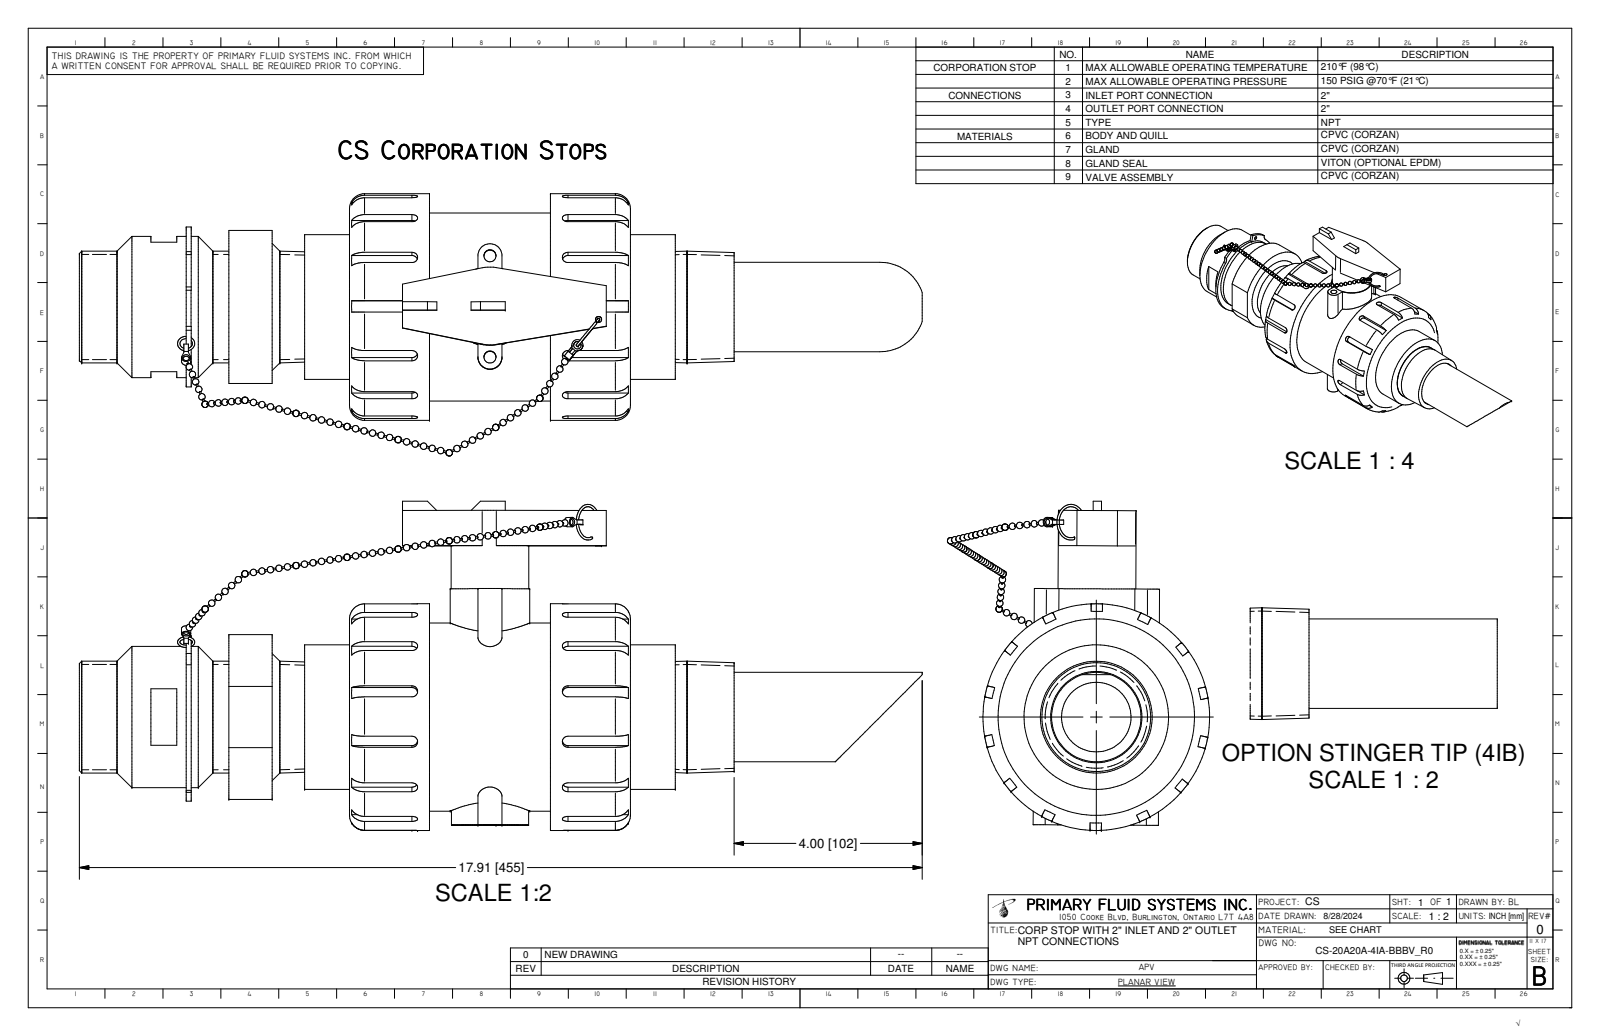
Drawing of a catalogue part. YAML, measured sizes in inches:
step_written_by: "Autodesk Inventor 2025 (CONFIG_CONTROL_DESIGN)"
units: inches
bodies: {solids: 19, faces: 431, planar: 211, cylindrical: 142, other: 78}
overall_size: [17.91, 6.994, 5.571]
volume: 136.3
surface_area: 488
round_holes:
  - {diameter: 0.118, count: 2}
  - {diameter: 0.15, count: 2}
  - {diameter: 0.157, count: 2}
  - {diameter: 0.256, count: 2}
  - {diameter: 0.13, count: 1}
  - {diameter: 1.27, count: 1}
  - {diameter: 1.476, count: 1}
  - {diameter: 1.5, count: 1}
  - {diameter: 1.93, count: 1}
  - {diameter: 1.939, count: 1}
  - {diameter: 2.375, count: 1}
  - {diameter: 2.982, count: 1}
round_bosses_or_shafts:
  - {diameter: 0.035, count: 9}
  - {diameter: 0.236, count: 2}
  - {diameter: 4.815, count: 1}
  - {diameter: 3.996, count: 1}
  - {diameter: 3.071, count: 1}
  - {diameter: 3, count: 1}
  - {diameter: 2.72, count: 1}
  - {diameter: 2.254, count: 1}
partial_cylinders:
  - {radius: 0.12, count: 26}
  - {radius: 0.059, count: 2}
  - {radius: 0.098, count: 2}
  - {radius: 0.236, count: 2}
  - {radius: 0.256, count: 2}
  - {radius: 1.698, count: 1}
  - {radius: 1.75, count: 1}
  - {radius: 1.784, count: 1}
face_to_face_distances: [1.7, 4.268, 0.953, 2.653, 5.221, 6.921, 5.968, 2.568, 2.564, 4.264]
hole_center_spacings: [1.074, 1.638, 0.314, 0.708, 1.24, 1.506, 1.872, 1.911]
